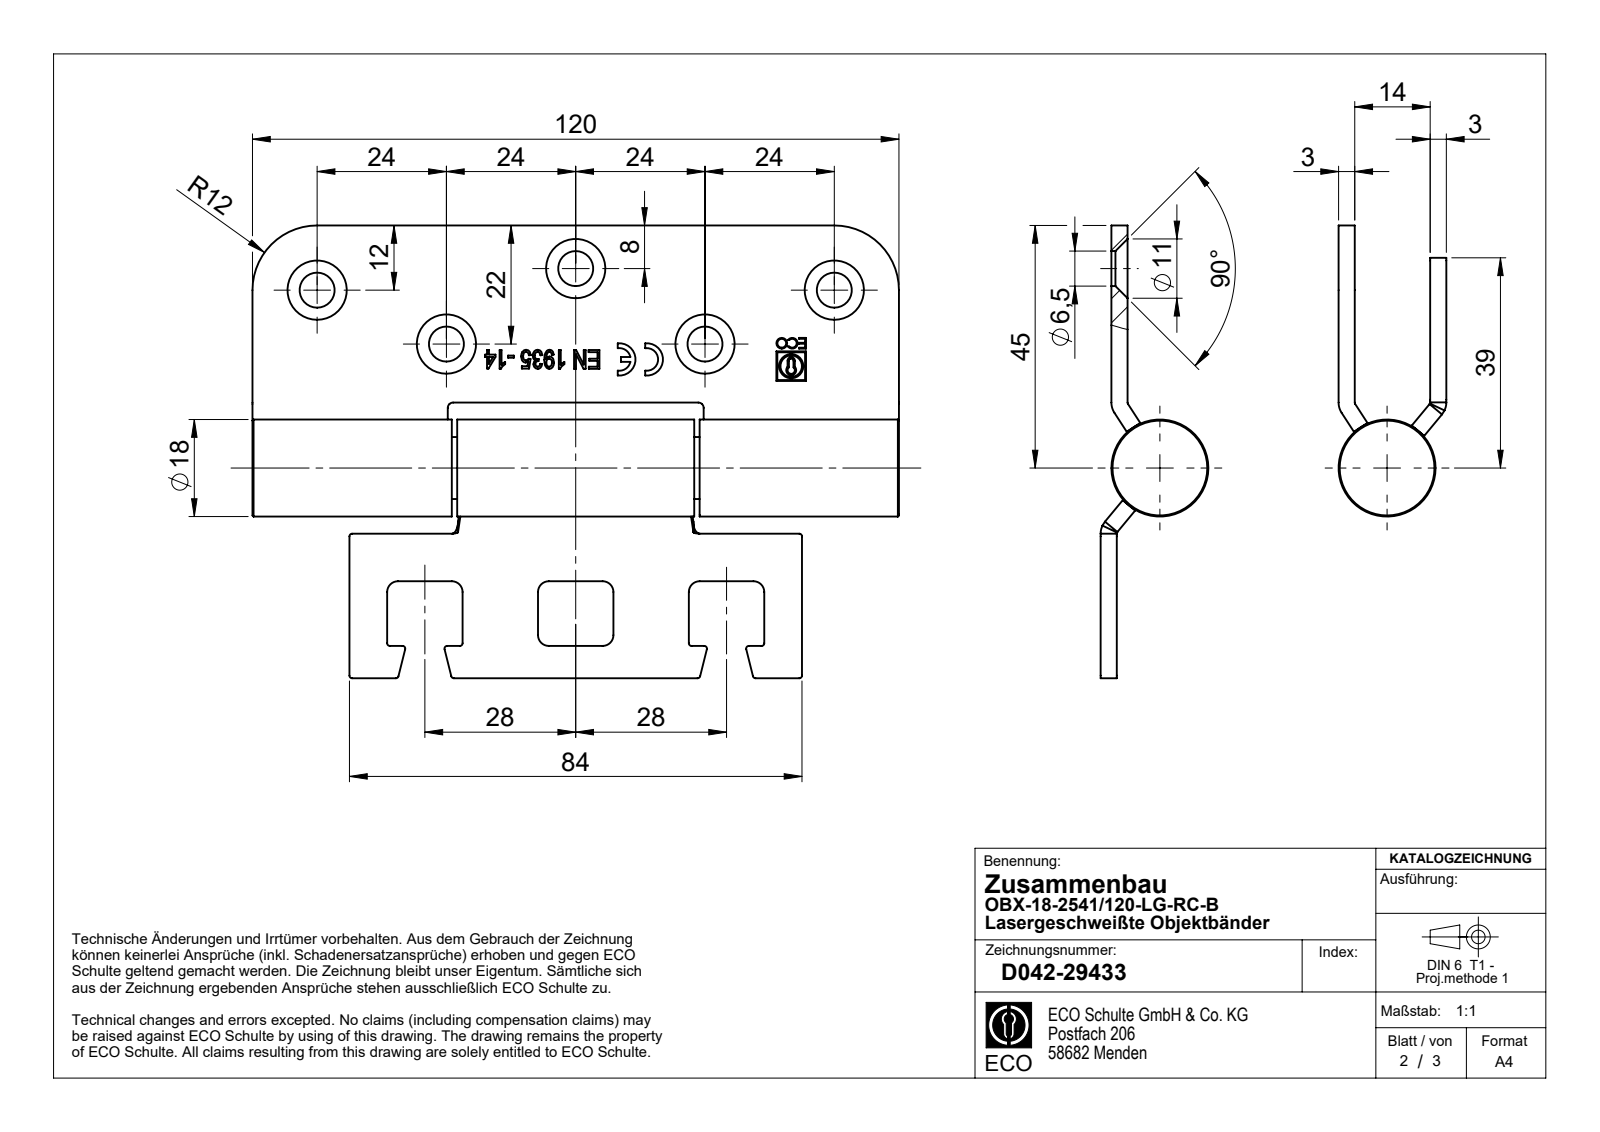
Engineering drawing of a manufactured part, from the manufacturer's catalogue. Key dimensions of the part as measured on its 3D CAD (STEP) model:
Part name (STEP PRODUCT): B01572; D043-25261; D046-14312; DIN5401-III (+4 more)
STEP written by: SolidWorks 2017 (AUTOMOTIVE_DESIGN)
Units: millimetres
Bodies: 11 solids, 462 faces (216 planar, 138 cylindrical, 108 other)
Overall size (bounding box): 120 × 54 × 20
Volume: 47 578 mm³ · Surface area: 28 760 mm²
Round holes (diameter × count): ⌀6.5 ×5, ⌀2 ×2, ⌀0.5 ×1, ⌀4.5 ×1, ⌀7.9 ×1
Round bosses / shafts (diameter × count): ⌀18 ×1, ⌀12 ×1, ⌀11.8 ×1, ⌀11.5 ×1, ⌀7.7 ×1, ⌀4 ×1, ⌀1.65 ×1
Partial cylindrical surfaces — rounded edges, fillets, slot ends (radius × count): R0.5 ×18, R2 ×8, R0.25 ×6, R0.68 ×2, R1 ×2, R2.1 ×2, R3 ×2, R3.5 ×2
Main face-to-face distances: 3, 17, 20, 14, 82, 11.5, 108.5, 1, 12, 6
Hole centre spacings: 26, 27.78, 48.17, 72.69, 1.95, 4.25, 4.6, 12.56
